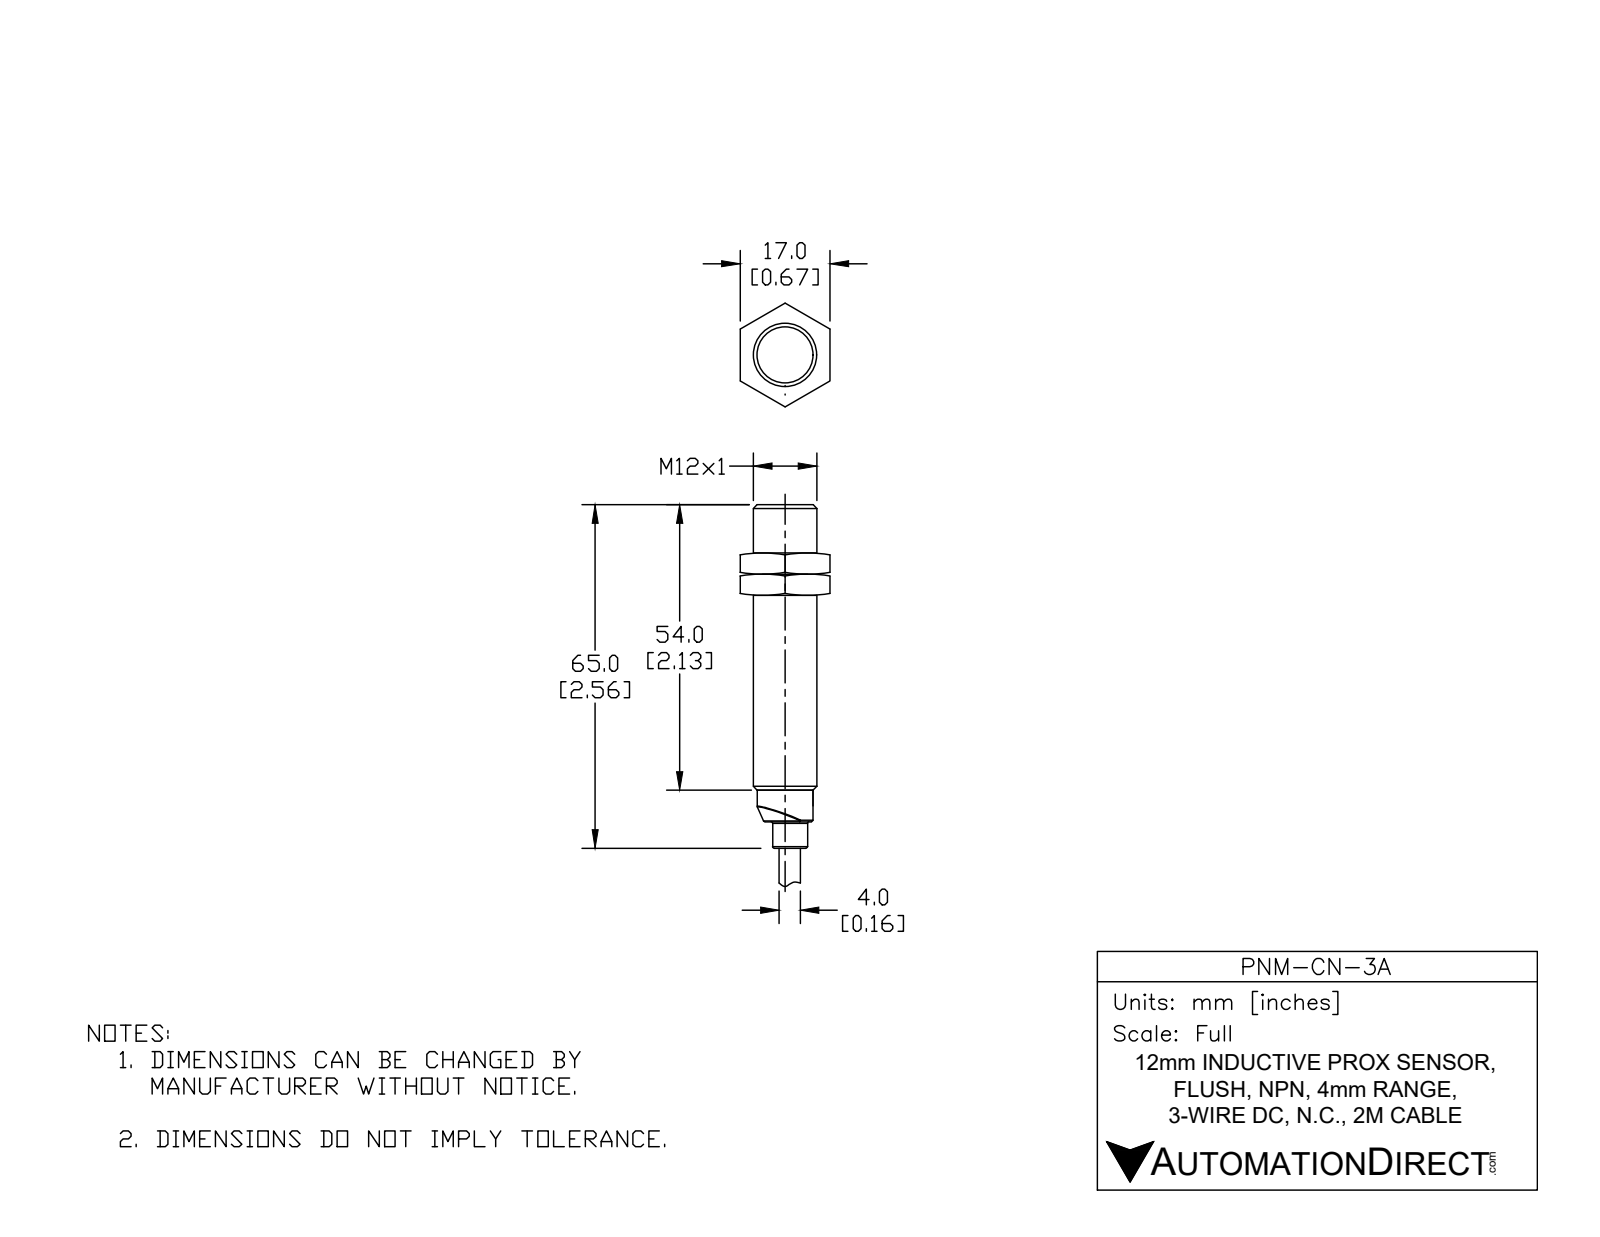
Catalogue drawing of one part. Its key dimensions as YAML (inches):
part_name: "PNM-CN-3A"
step_written_by: "SolidWorks 2017 (AUTOMOTIVE_DESIGN)"
units: inches
bodies: {solids: 1, faces: 68, planar: 21, cylindrical: 19, other: 28}
overall_size: [4.559, 0.472, 0.472]
volume: 0.452
surface_area: 4.972
round_holes:
  - {diameter: 0.161, count: 1}
  - {diameter: 0.401, count: 1}
round_bosses_or_shafts:
  - {diameter: 0.472, count: 1}
  - {diameter: 0.417, count: 1}
  - {diameter: 0.415, count: 1}
  - {diameter: 0.384, count: 1}
  - {diameter: 0.26, count: 1}
  - {diameter: 0.157, count: 1}
partial_cylinders:
  - {radius: 0.091, count: 1}
face_to_face_distances: [2.362, 2.559, 0.197, 4.559, 2.197, 2, 0.022, 2.34, 2.537, 4.537]
hole_center_spacings: [0.039]
